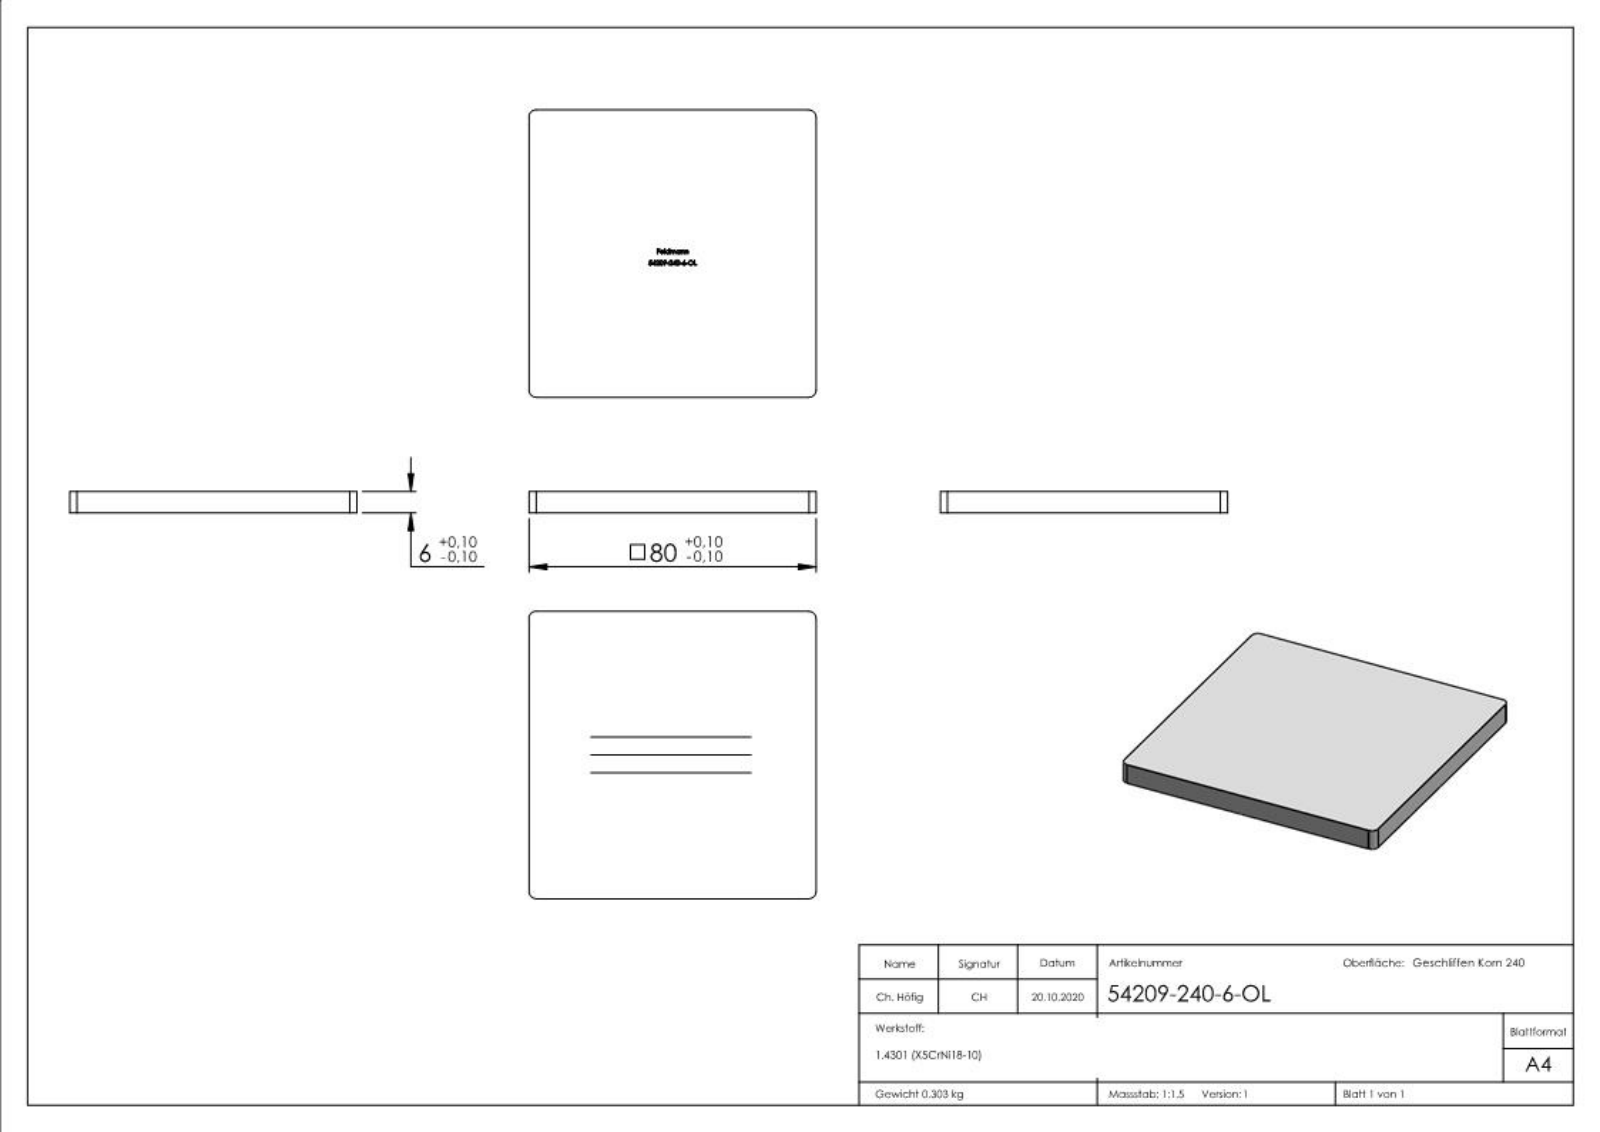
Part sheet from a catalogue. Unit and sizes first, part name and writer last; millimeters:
Units: millimetres
Overall size (bounding box): 80 × 80 × 6
Partial cylindrical surfaces — rounded edges, fillets, slot ends (radius × count): R2 ×4
Main face-to-face distances: 6, 80, 5.9, 0.44, 36.81, 43.19, 37.25, 42.75, 0.58, 40
Volume: 38 379 mm³ · Surface area: 14 704 mm²
Bodies: 1 solid, 276 faces (160 planar, 4 cylindrical, 112 other)
Part name (STEP PRODUCT): 54209-240-6-OL
STEP written by: SolidWorks 2018 (CONFIG_CONTROL_DESIGN)
